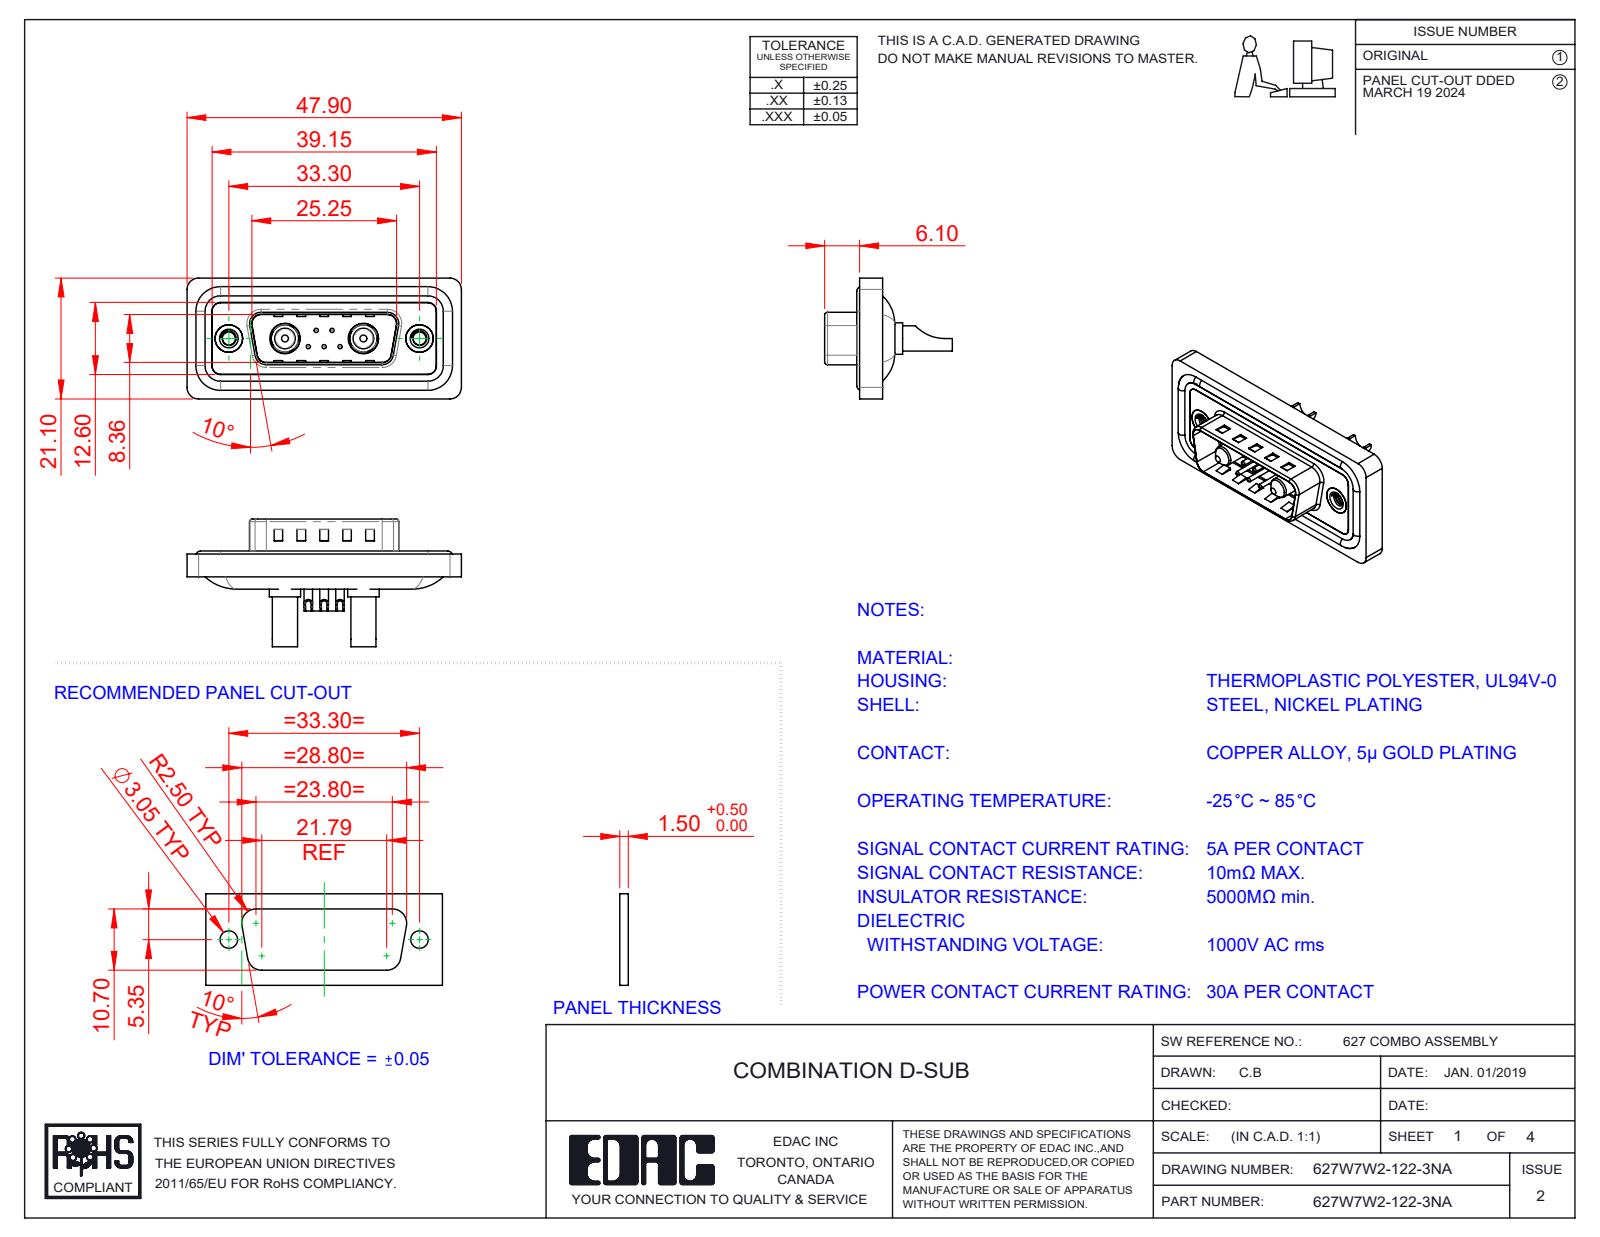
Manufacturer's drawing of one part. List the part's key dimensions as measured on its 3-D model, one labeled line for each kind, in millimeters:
Part name (STEP PRODUCT): 627Combo Shell Front_15 Contacts; 627Combo Housing_7W2; 627W7W2-122-3NA; 627Combo Threaded Rivet_A (+5 more)
STEP written by: SolidWorks 2023 (CONFIG_CONTROL_DESIGN)
Units: millimetres
Bodies: 16 solids, 720 faces (248 planar, 310 cylindrical, 162 other)
Overall size (bounding box): 47.9 × 22.3 × 21.1
Volume: 5 574 mm³ · Surface area: 9 045 mm²
Round holes (diameter × count): ⌀0.75 ×5, ⌀1 ×5, ⌀1.6 ×5, ⌀2 ×5, ⌀2.26 ×2, ⌀3.5 ×2, ⌀4 ×2, ⌀4.8 ×2, ⌀4.85 ×2, ⌀5 ×2, ⌀5.3 ×2
Round bosses / shafts (diameter × count): ⌀1.5 ×5, ⌀1.6 ×4, ⌀5.5 ×2, ⌀5.2 ×2, ⌀4.9 ×2, ⌀4.75 ×2, ⌀4.4 ×2, ⌀3.75 ×2
Partial cylindrical surfaces — rounded edges, fillets, slot ends (radius × count): R1.5 ×26, R2 ×20, R0.5 ×8, R1.6 ×8, R1 ×6, R0.25 ×4, R0.6 ×4, R0.65 ×4
Main face-to-face distances: 0.4, 1.1, 1.6, 1.5, 0.5, 3.1, 2.9, 0.82, 9.58, 2.5
Hole centre spacings: 3.16, 2.77, 9.8, 23.5, 4.31, 4.33, 5.03, 5.04
